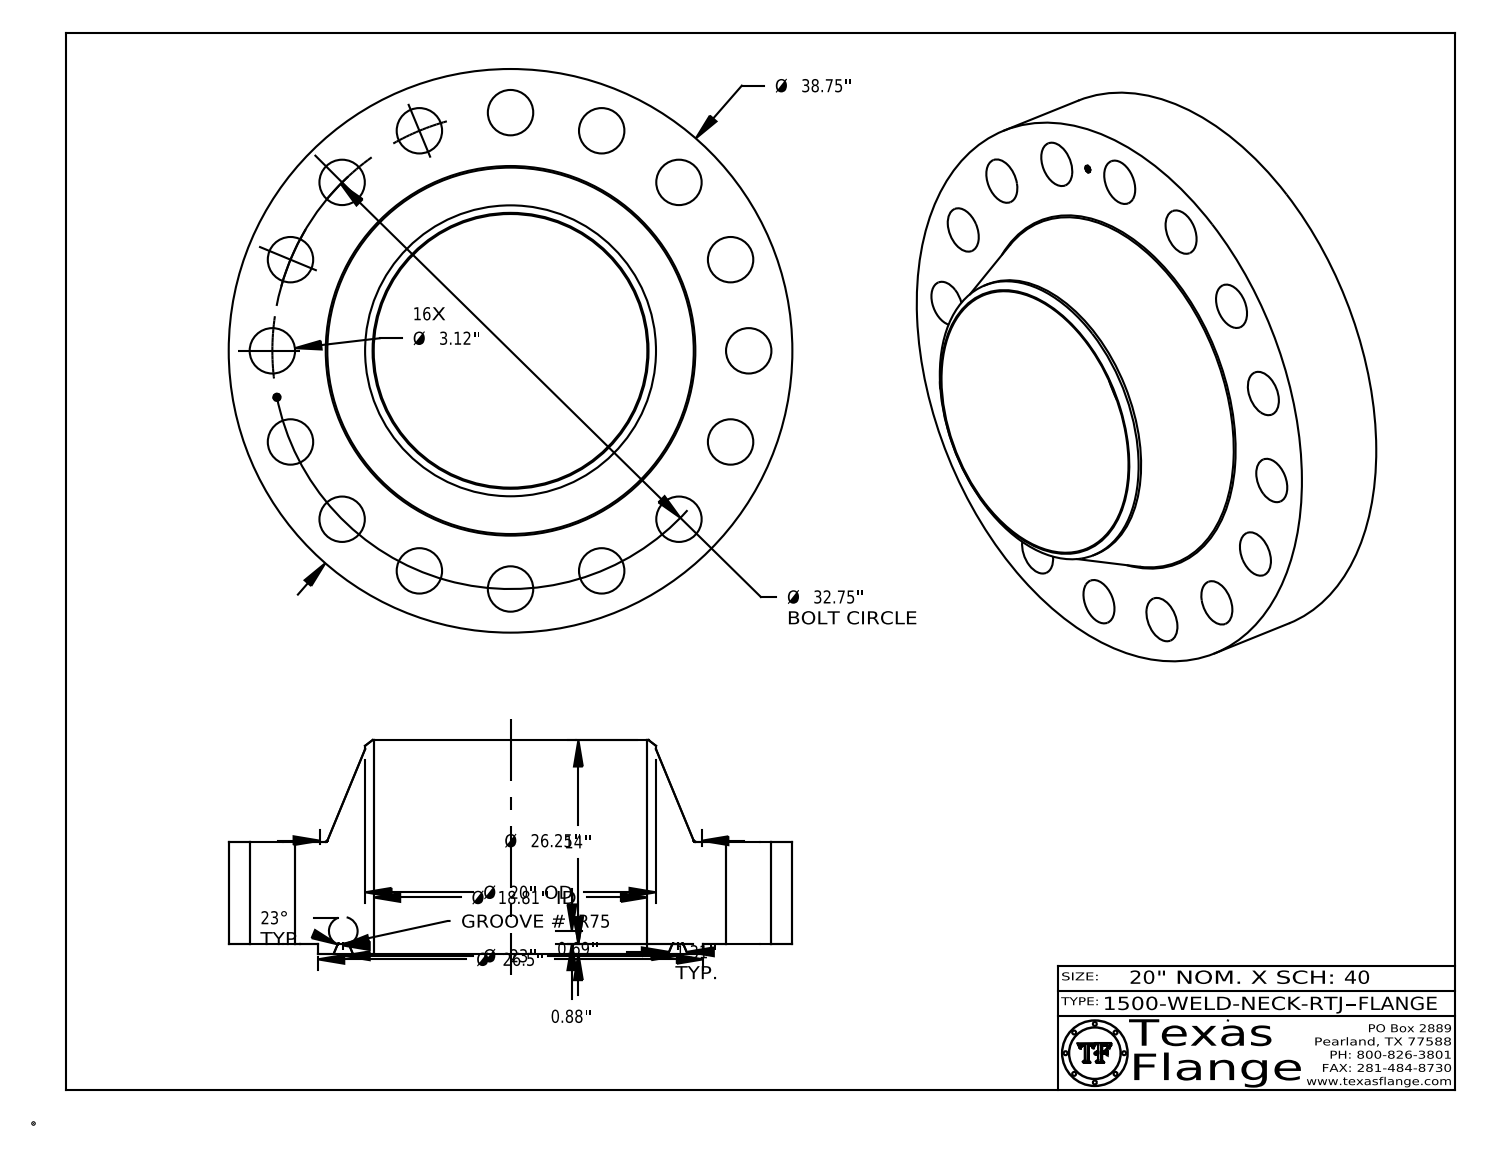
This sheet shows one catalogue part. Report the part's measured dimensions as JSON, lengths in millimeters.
{"part_name": "1500-WELD-NECK-RTJ", "step_written_by": "CATIA V5 STEP AP214 (AUTOMOTIVE_DESIGN)", "units": "millimeters", "bodies": {"solids": 1, "faces": 445, "planar": 371, "cylindrical": 60, "other": 14}, "overall_size": [984.3, 984.3, 373.1], "volume_mm3": 105000000, "surface_area_mm2": 3111000, "round_holes": [[79.2, 16], [12.6, 1], [477.8, 1]], "round_bosses_or_shafts": [[0.8, 8], [984.3, 1], [673.1, 1], [508, 1], [9.9, 1]], "face_to_face_distances": [177.8, 17.5, 195.3, 373.1, 355.6, 194.9, 177.4, 0.4, 178.2, 3.8], "hole_center_spacings": [462.2, 415.9, 318.3, 588.2, 768.5, 162.3, 162.3, 691.6]}
